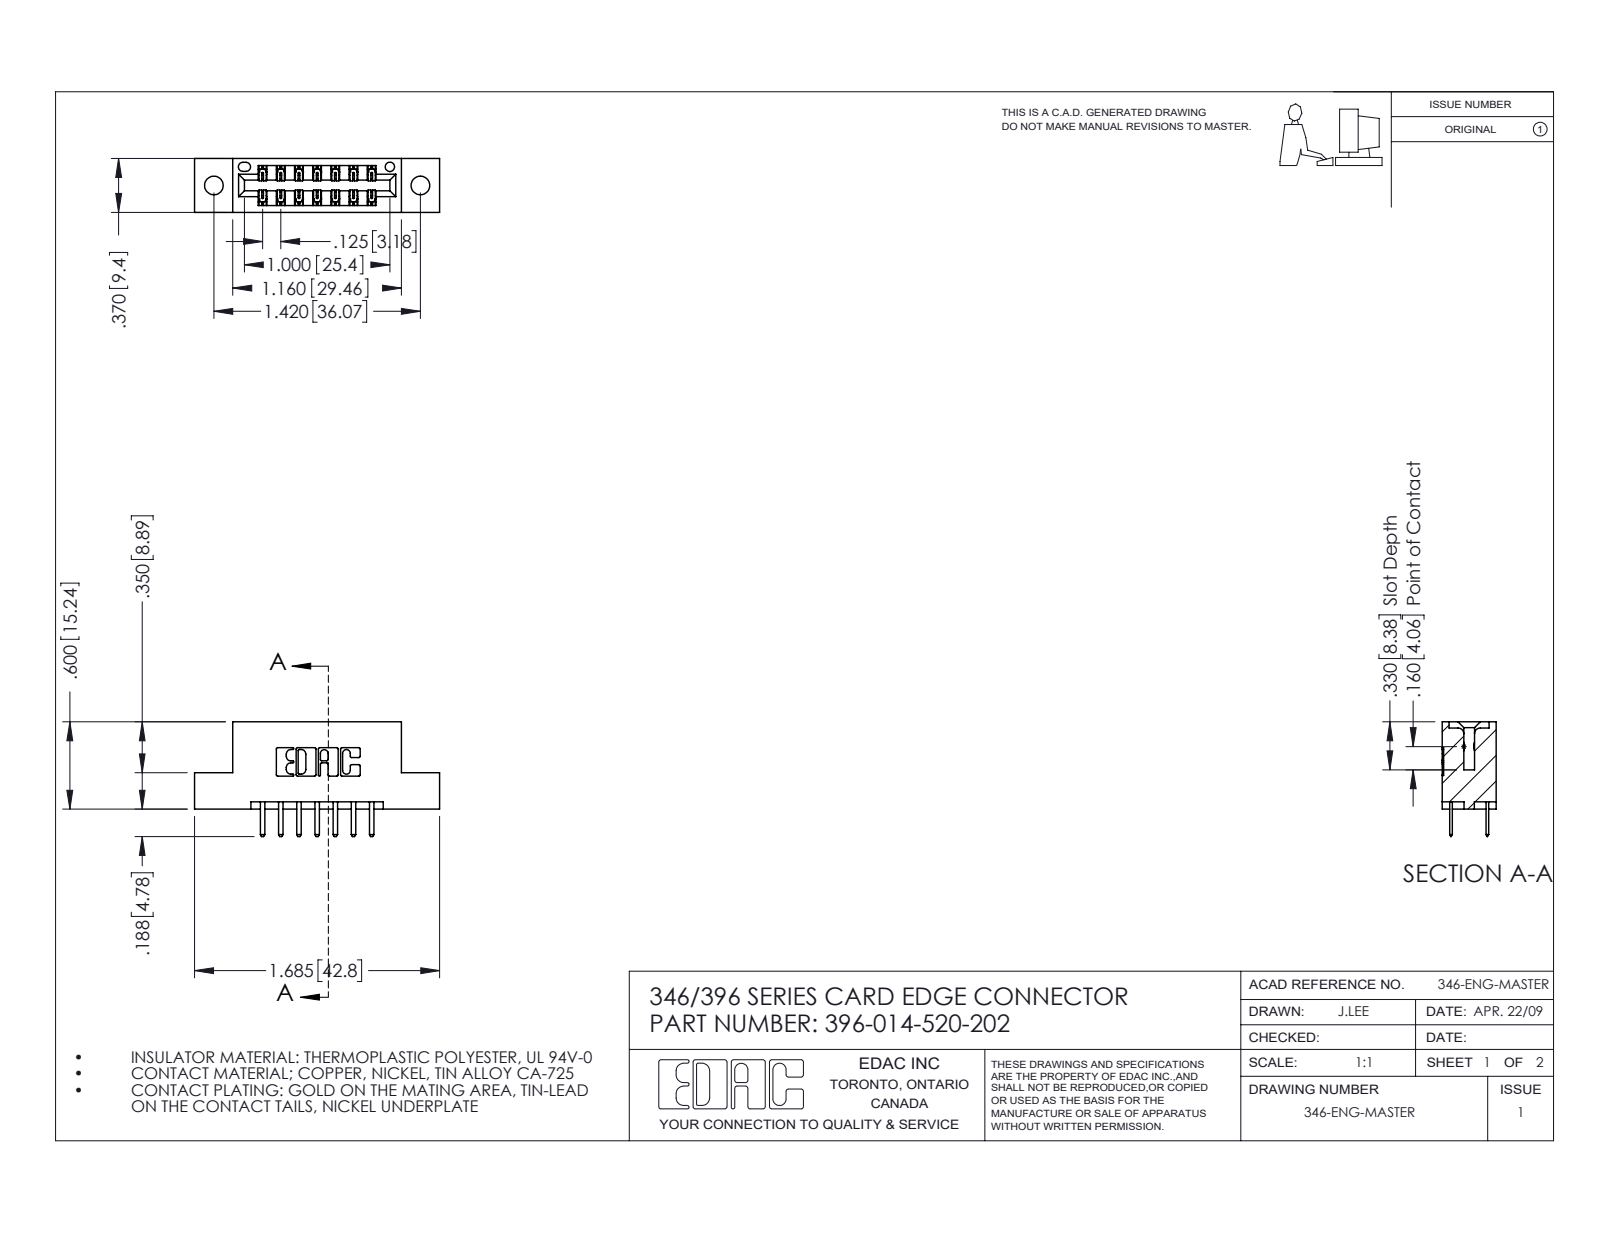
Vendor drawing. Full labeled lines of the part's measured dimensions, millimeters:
Part name (STEP PRODUCT): 345-292-001_345-293-120; 396-014-520-202; 346 Part_Flush Mounting Lugs - 0.128 Dia
STEP written by: SolidWorks 2016 (CONFIG_CONTROL_DESIGN)
Units: millimetres
Bodies: 15 solids, 906 faces (594 planar, 312 cylindrical, 0 other)
Overall size (bounding box): 42.8 × 20 × 9.4
Volume: 3 850 mm³ · Surface area: 4 470 mm²
Round holes (diameter × count): ⌀3.3 ×2, ⌀1.6 ×1
Partial cylindrical surfaces — rounded edges, fillets, slot ends (radius × count): R0.3 ×22, R0.2 ×21, R0.3 ×18, R0.2 ×6, R0.8 ×6, R0.7 ×3, R0.4 ×2, R0.6 ×2
Main face-to-face distances: 6.4, 9.4, 1.2, 8.2, 3.8, 5.6, 2.5, 4.4, 3.2, 4.7
Hole centre spacings: 6.2, 30.9, 36.1
